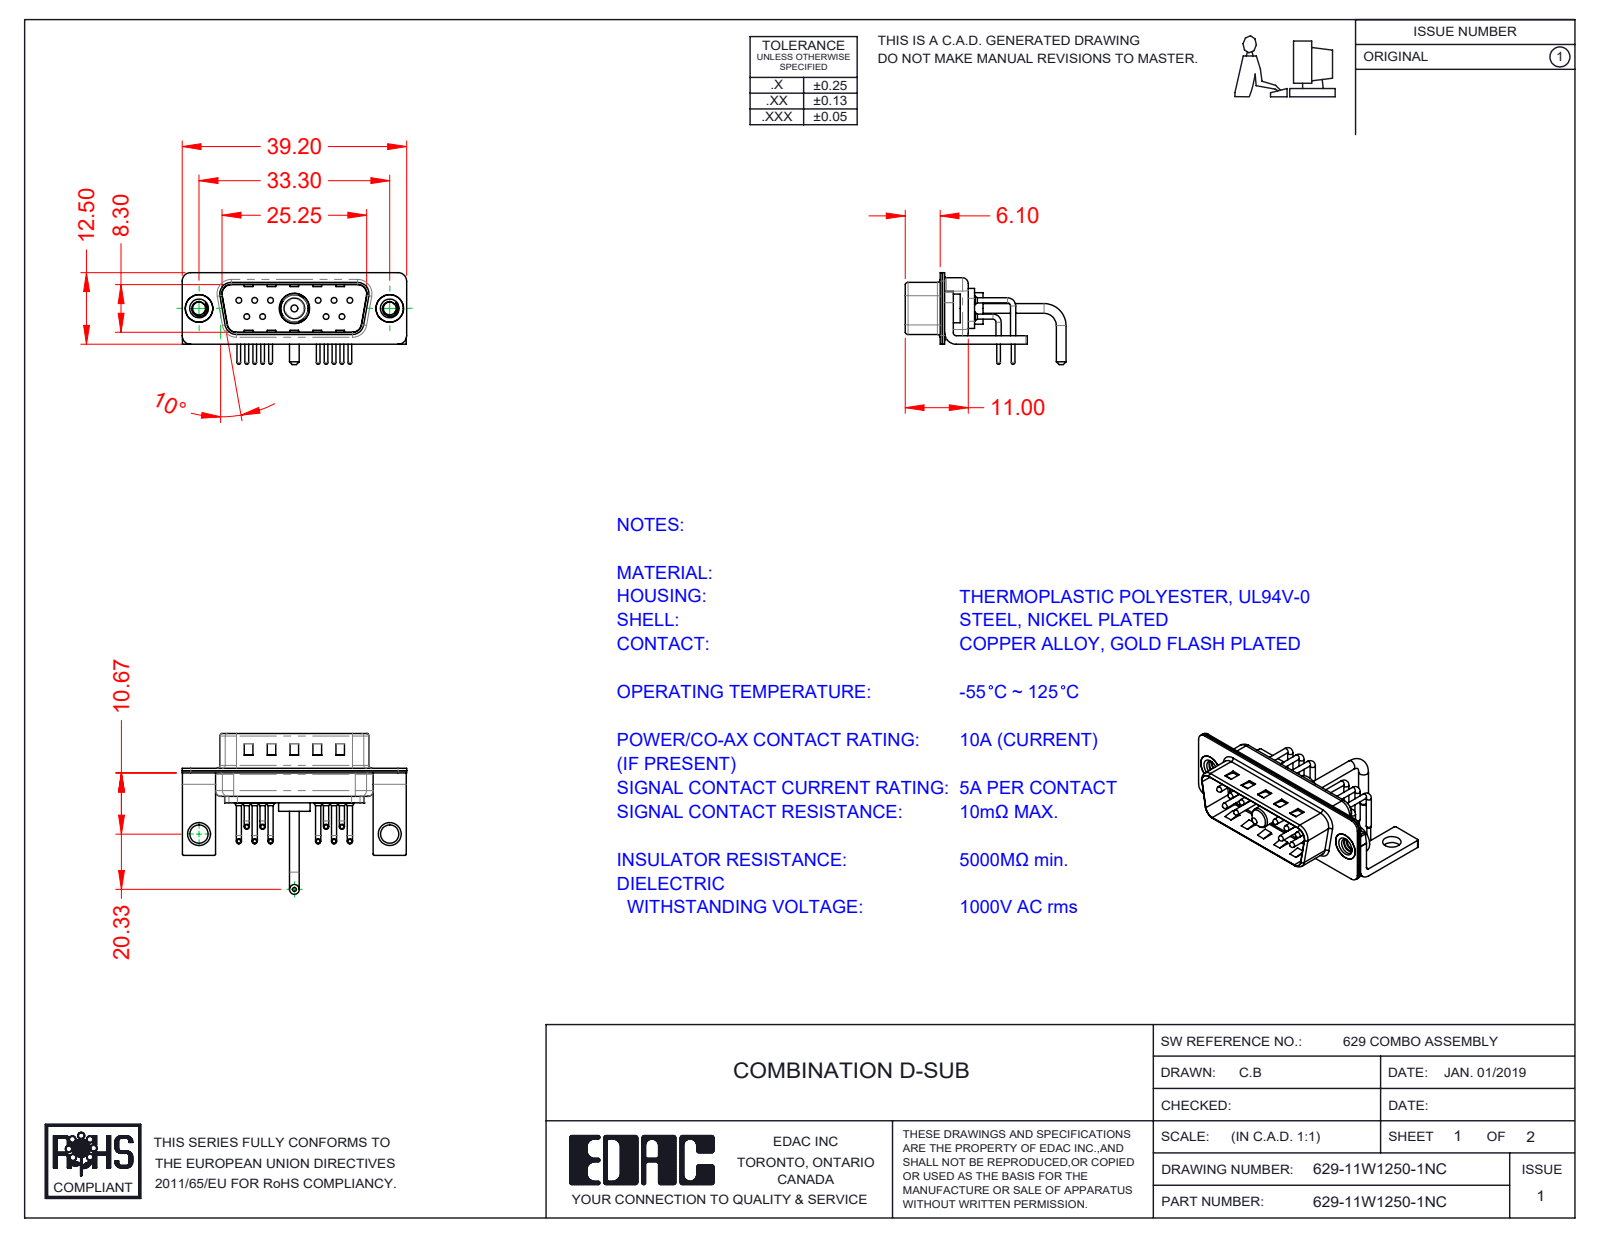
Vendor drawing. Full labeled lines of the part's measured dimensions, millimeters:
Part name (STEP PRODUCT): 629Combo Shell Rear_15 Contacts; 629Combo Contact Row 1; 629Combo Shell Front_15 Contacts; 629-11W1250-1NC (+5 more)
STEP written by: SolidWorks 2020 (CONFIG_CONTROL_DESIGN)
Units: millimetres
Bodies: 19 solids, 1544 faces (818 planar, 542 cylindrical, 184 other)
Overall size (bounding box): 39.2 × 28.08 × 16.05
Volume: 2 333 mm³ · Surface area: 5 863 mm²
Round holes (diameter × count): ⌀0.75 ×10, ⌀1.6 ×10, ⌀2 ×10, ⌀2.26 ×2, ⌀3.2 ×2, ⌀4 ×2, ⌀4.8 ×2, ⌀4.85 ×1, ⌀5.3 ×1
Round bosses / shafts (diameter × count): ⌀0.9 ×20, ⌀1.5 ×10, ⌀1 ×10, ⌀0.65 ×10, ⌀5 ×2, ⌀4.9 ×2, ⌀1.7 ×2, ⌀5.5 ×1
Partial cylindrical surfaces — rounded edges, fillets, slot ends (radius × count): R0.25 ×16, R1.5 ×16, R2 ×13, R1.01 ×10, R0.5 ×9, R1.6 ×8, R1 ×7, R0.6 ×4
Main face-to-face distances: 0.4, 0.8, 1.5, 9.5, 9.1, 0.6, 8.7, 9.9, 1.2, 5.2
Hole centre spacings: 3.16, 2.77, 13.85, 11.08, 16.62, 5.03, 5.04, 5.54
